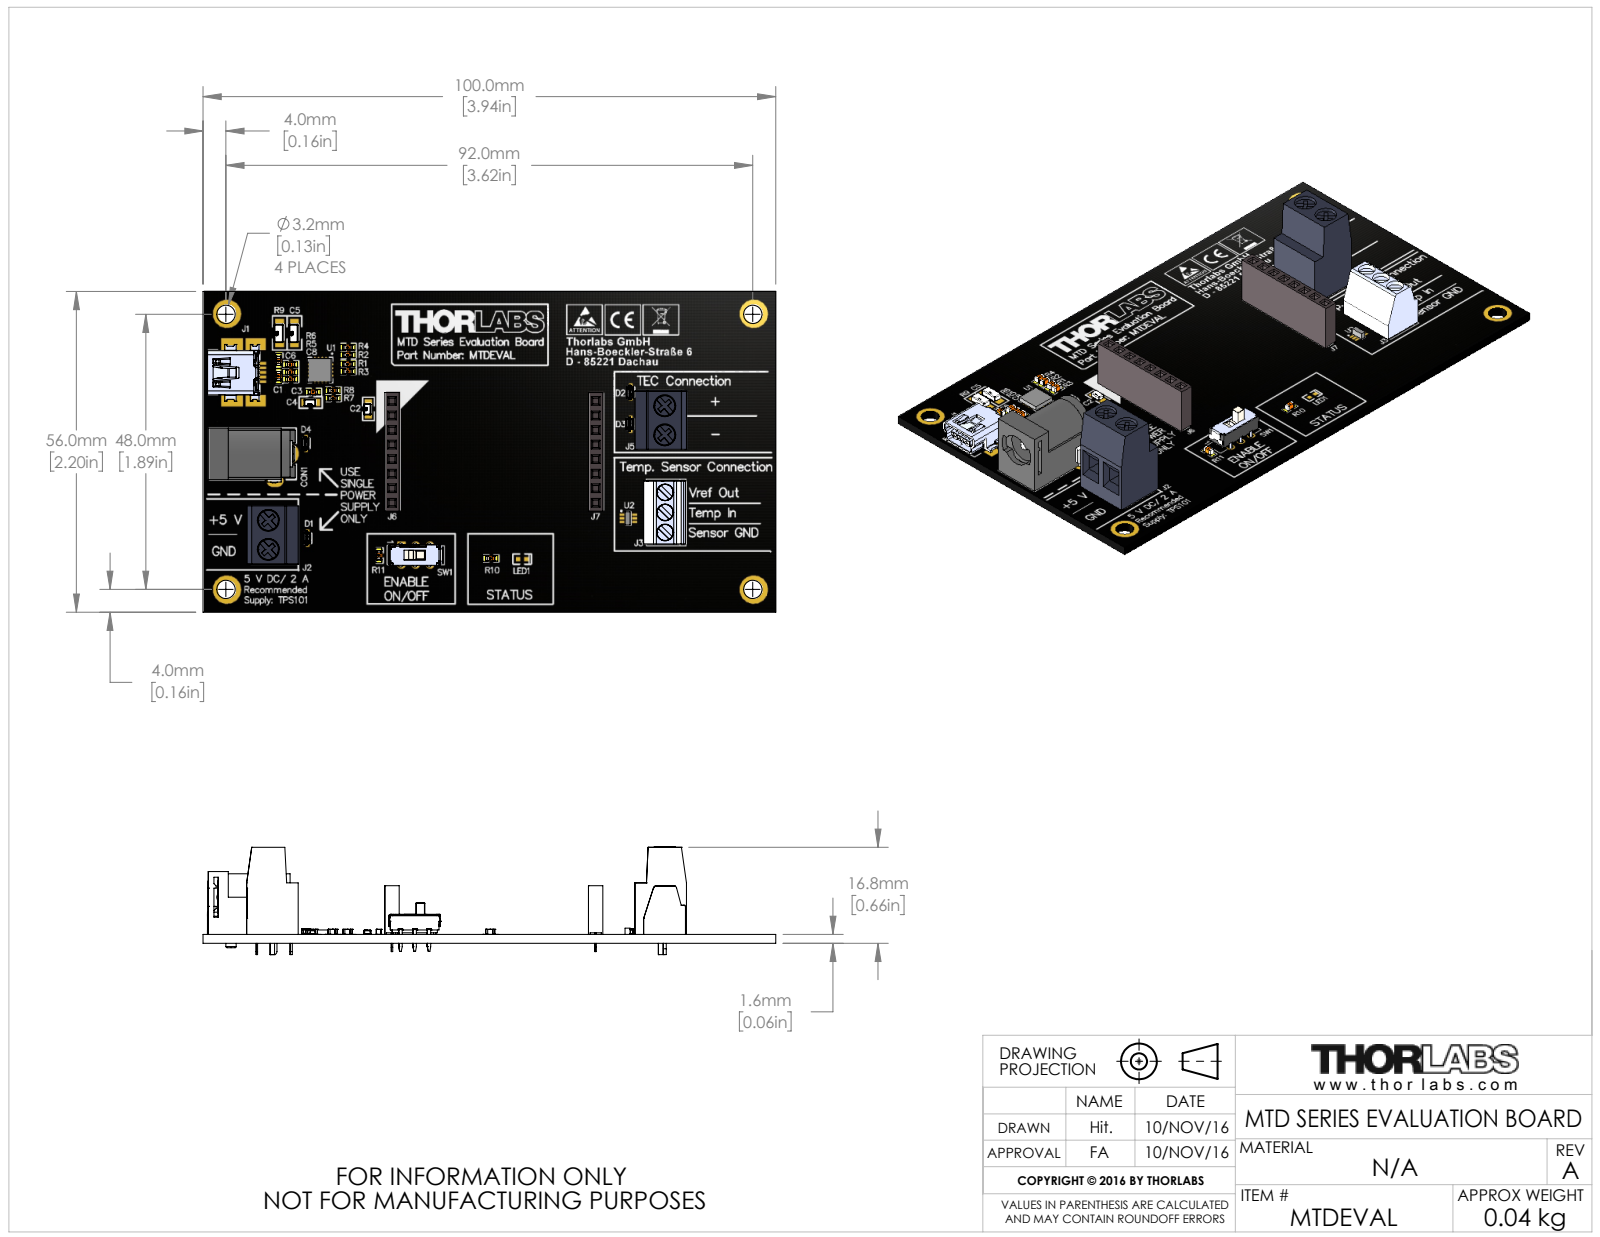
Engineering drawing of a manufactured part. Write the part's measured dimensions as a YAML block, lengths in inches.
part_name: "MTN007869-E0W"
step_written_by: "SolidWorks 2016 (AUTOMOTIVE_DESIGN)"
units: inches
bodies: {solids: 0, faces: 3245, planar: 2044, cylindrical: 654, other: 547}
overall_size: [3.937, 2.205, 0.736]
round_holes:
  - {diameter: 0.035, count: 24}
  - {diameter: 0.047, count: 4}
  - {diameter: 0.055, count: 4}
  - {diameter: 0.126, count: 4}
  - {diameter: 0.15, count: 4}
  - {diameter: 0.114, count: 3}
  - {diameter: 0.075, count: 1}
  - {diameter: 0.224, count: 1}
round_bosses_or_shafts:
  - {diameter: 0.139, count: 4}
  - {diameter: 0.11, count: 3}
  - {diameter: 0.043, count: 3}
  - {diameter: 0.031, count: 2}
  - {diameter: 0.118, count: 1}
  - {diameter: 0.106, count: 1}
  - {diameter: 0.079, count: 1}
  - {diameter: 0.071, count: 1}
partial_cylinders:
  - {radius: 0.006, count: 50}
  - {radius: 0.004, count: 32}
  - {radius: 0.008, count: 18}
  - {radius: 0.02, count: 17}
  - {radius: 0.012, count: 12}
  - {radius: 0.006, count: 10}
  - {radius: 0.059, count: 10}
  - {radius: 0.028, count: 8}
face_to_face_distances: [0.061, 0.098, 1.4, 0.789, 0.354, 0.4, 1.302, 1.189, 1.498, 0.598]
hole_center_spacings: [0.1, 1.404, 0.2, 1.414, 0.3, 1.432, 0.4, 1.4]
